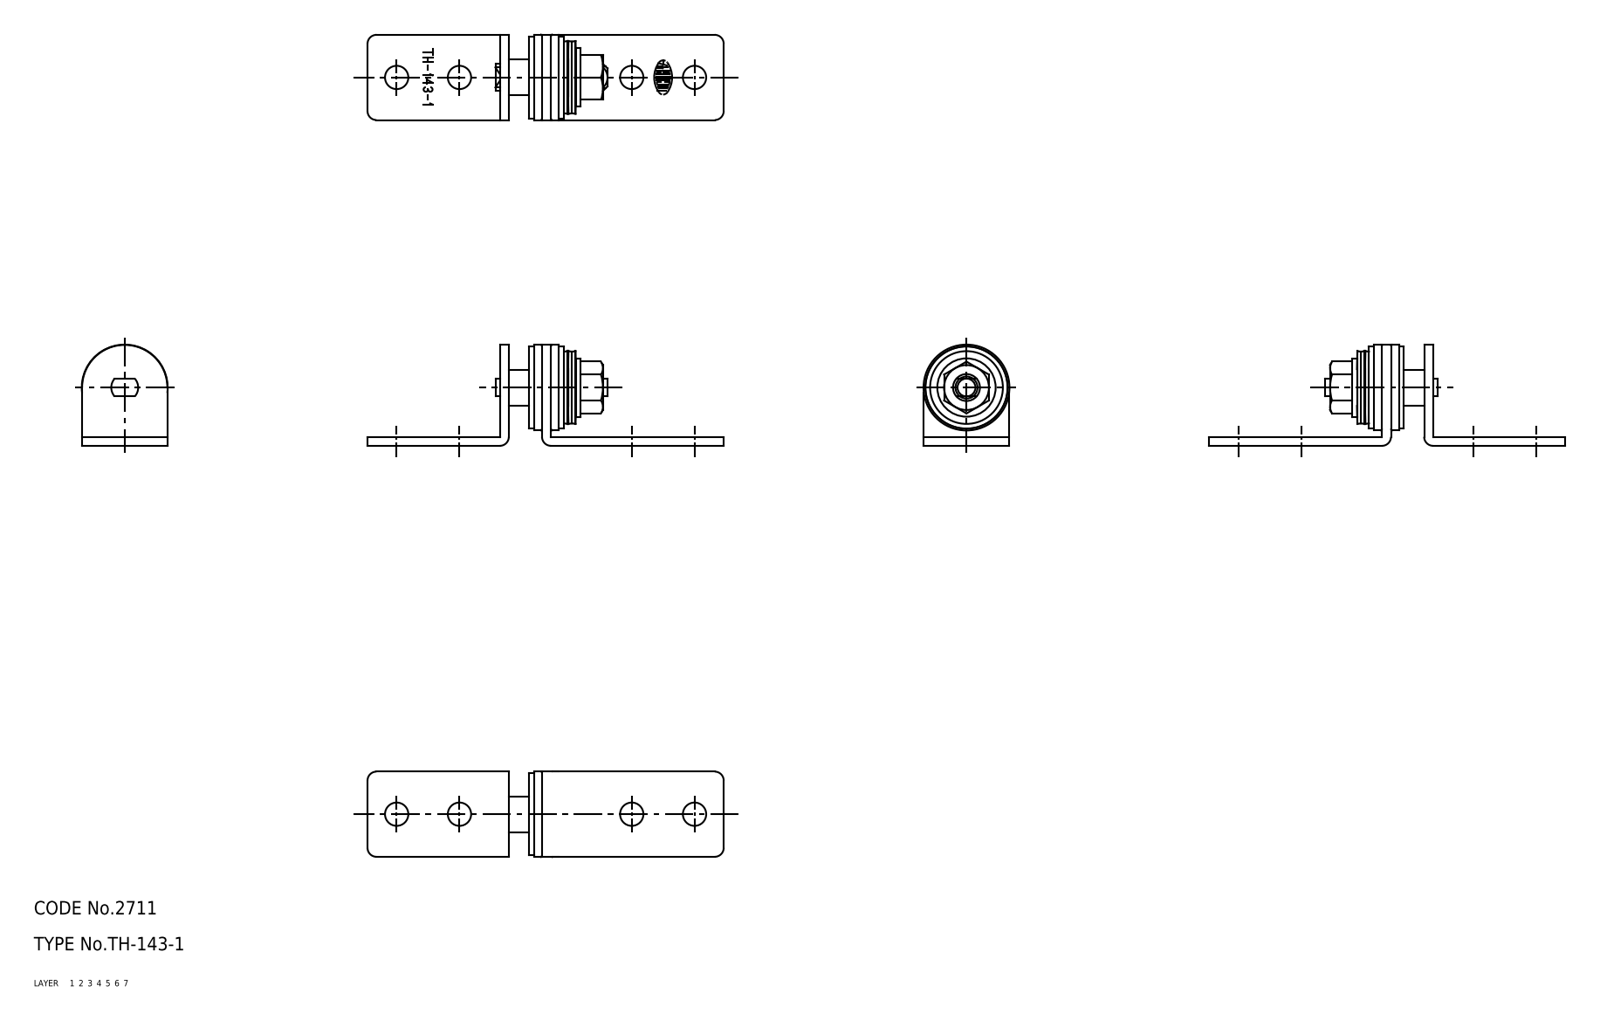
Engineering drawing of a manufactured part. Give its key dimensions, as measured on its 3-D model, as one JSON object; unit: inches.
{"part_name": "67117753; 67117766; 67117779; 67117792 (+8 more)", "step_written_by": "CADfix (AUTOMOTIVE_DESIGN)", "units": "inches", "bodies": {"solids": 12, "faces": 149, "planar": 0, "cylindrical": 0, "other": 149}, "overall_size": [3.126, 0.889, 0.754], "volume_in3": 0.413, "surface_area_in2": 14.79}
